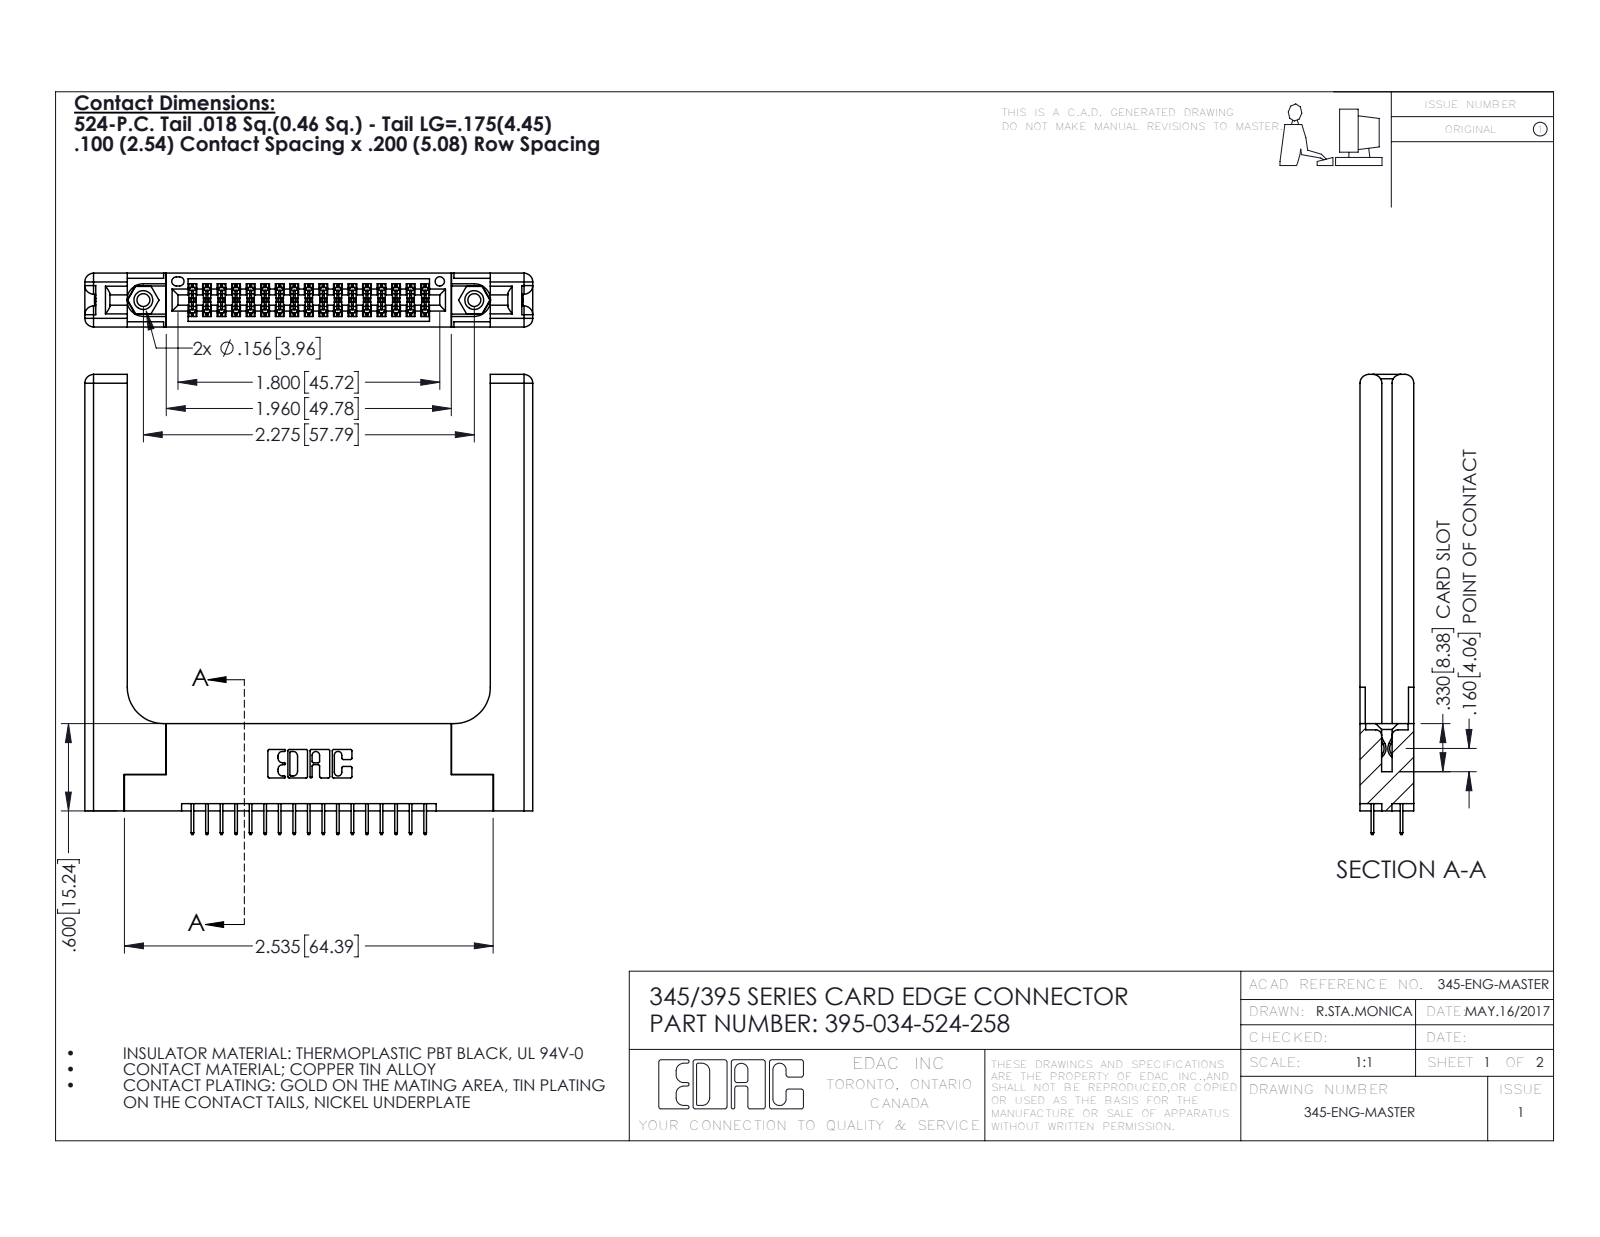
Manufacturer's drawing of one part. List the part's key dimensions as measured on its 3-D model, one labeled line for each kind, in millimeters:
Part name (STEP PRODUCT): 345-250-001_345-250-001-102; 395-034-524-258; 345-220-058_345-220-058; 345-292-001_345-293-124 (+1 more)
STEP written by: SolidWorks 2016 (CONFIG_CONTROL_DESIGN)
Units: millimetres
Bodies: 39 solids, 2218 faces (1554 planar, 604 cylindrical, 60 other)
Overall size (bounding box): 80.3 × 78.2 × 9.4
Volume: 15 800 mm³ · Surface area: 15 250 mm²
Round holes (diameter × count): ⌀2.3 ×2, ⌀3.2 ×2, ⌀4 ×2, ⌀1.6 ×1
Round bosses / shafts (diameter × count): ⌀3.9 ×2
Partial cylindrical surfaces — rounded edges, fillets, slot ends (radius × count): R0.2 ×51, R0.3 ×22, R1.5 ×16, R0.2 ×6, R0.8 ×6, R0.7 ×3, R0.4 ×2, R0.5 ×2
Main face-to-face distances: 9.4, 1.8, 7.6, 5.1, 3.8, 3.8, 2, 5.6, 2.5, 6.9
Hole centre spacings: 6.9, 51.8, 57.8
